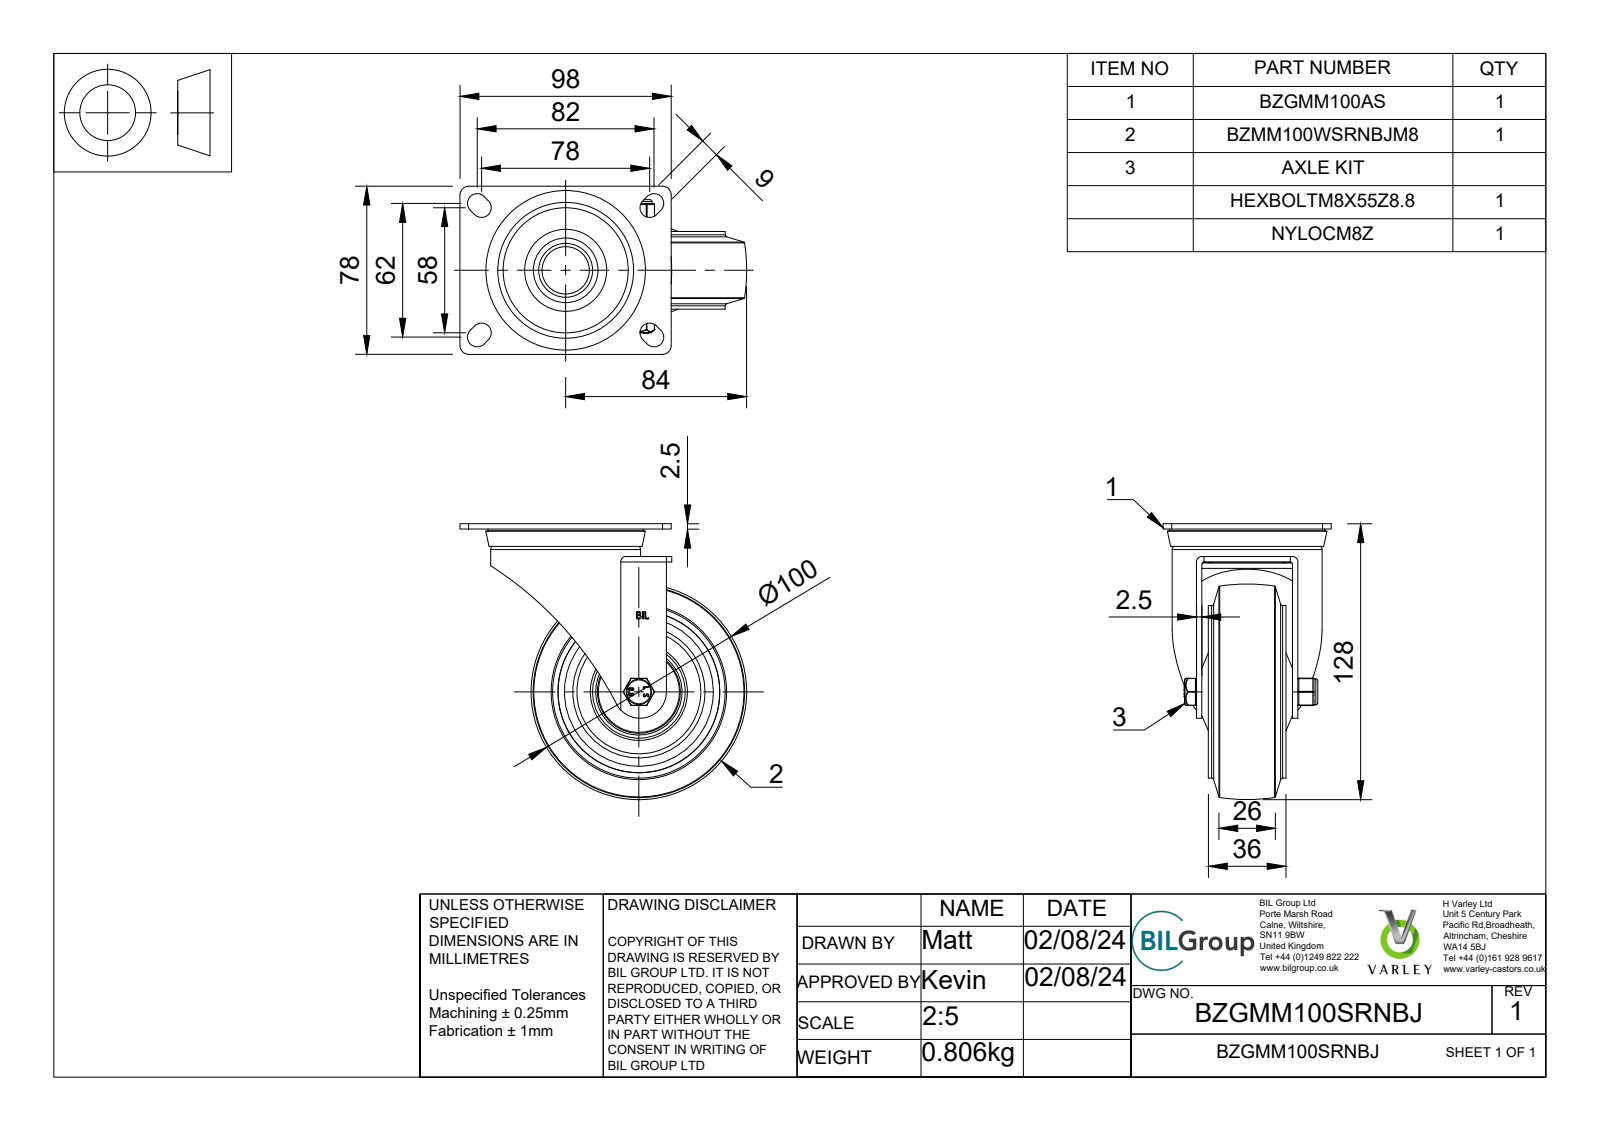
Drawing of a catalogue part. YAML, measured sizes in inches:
part_name: "BZGMM100SRNBJ v3; BZGMM100AS - 2 - 42 v1; ZINC PLATED, PRESSED STEEL TOP PLATE; ZINC PLATED, PRESSED STEEL TOP PLATE Geometry (+7 more)"
step_written_by: "Autodesk Translation Framework v13.14.0.145 (AUTOMOTIVE_DESIGN)"
units: inches
bodies: {solids: 51, faces: 768, planar: 272, cylindrical: 194, other: 302}
overall_size: [5.236, 5.039, 3.071]
volume: 16.14
surface_area: 203.9
round_holes:
  - {diameter: 0.026, count: 2}
  - {diameter: 1.024, count: 2}
  - {diameter: 1.181, count: 2}
  - {diameter: 0.315, count: 1}
  - {diameter: 0.323, count: 1}
  - {diameter: 0.339, count: 1}
  - {diameter: 0.591, count: 1}
  - {diameter: 0.787, count: 1}
  - {diameter: 0.886, count: 1}
  - {diameter: 1.22, count: 1}
  - {diameter: 1.26, count: 1}
  - {diameter: 1.299, count: 1}
round_bosses_or_shafts:
  - {diameter: 3.15, count: 1}
  - {diameter: 2.736, count: 1}
  - {diameter: 1.85, count: 1}
  - {diameter: 1.693, count: 1}
  - {diameter: 1.516, count: 1}
  - {diameter: 1.378, count: 1}
  - {diameter: 1.201, count: 1}
  - {diameter: 1.102, count: 1}
partial_cylinders:
  - {radius: 0.02, count: 18}
  - {radius: 0.01, count: 12}
  - {radius: 0.177, count: 8}
  - {radius: 0.013, count: 4}
  - {radius: 0.025, count: 4}
  - {radius: 0.049, count: 4}
  - {radius: 0.157, count: 4}
  - {radius: 0.025, count: 2}
face_to_face_distances: [0.098, 0.118, 0.217, 0.709, 1.752, 1.043, 1.535, 0.827, 0.394, 0.335]
hole_center_spacings: [0.127, 0.098]
